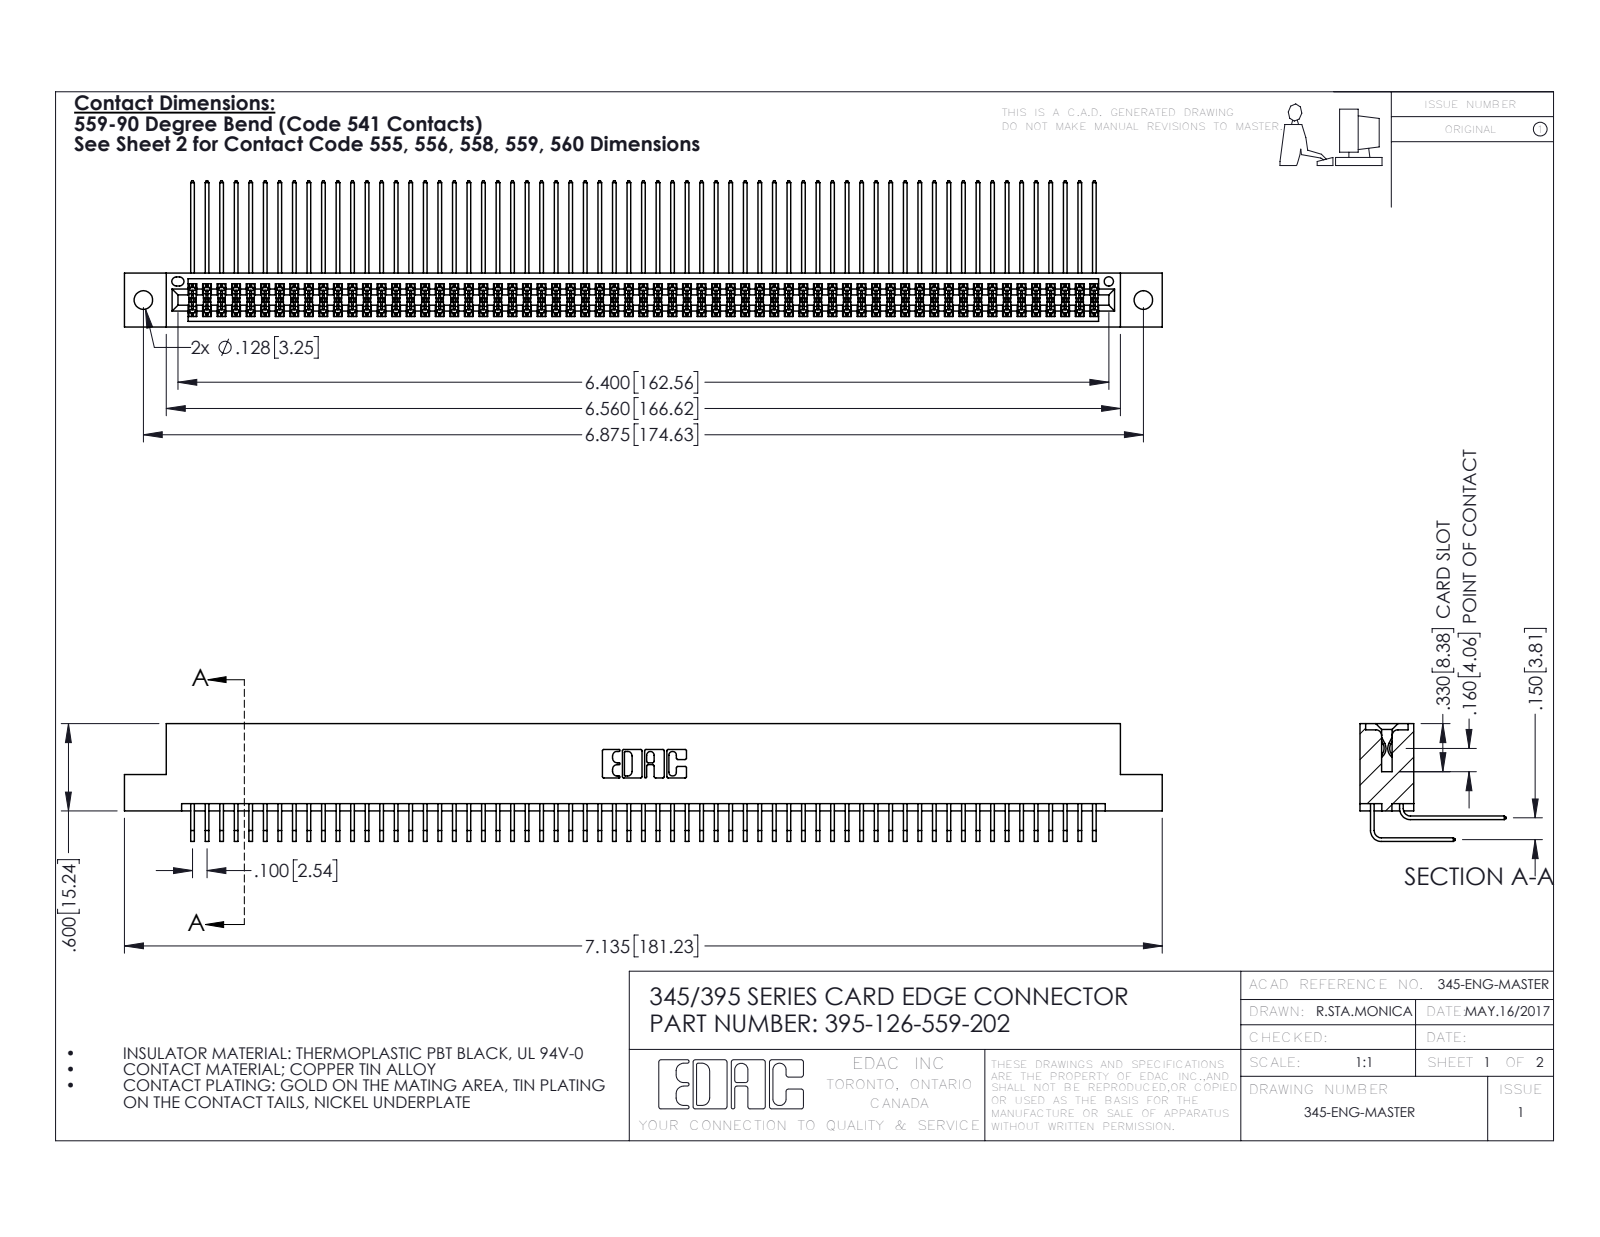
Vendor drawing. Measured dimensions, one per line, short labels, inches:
name: 345 Part_Flush Mounting Lugs - 0.128 Dia; 395-126-559-202; 345-292-001_558 559 Tail - 1; 345-292-001_559 Tail - 2
written by: SolidWorks 2016 (CONFIG_CONTROL_DESIGN)
unit: in
bodies: 127 solids, 6678 faces (4490 planar, 2188 cylindrical, 0 other)
size: 7.135 × 1.005 × 0.809
volume: 1.128 in³; area: 47.87 in²
holes: 2× ⌀0.128, 1× ⌀0.064
rounds: 190× R0.006, 22× R0.01, 6× R0.007, 6× R0.031, 3× R0.026, 2× R0.014, 2× R0.019, 2× R0.022
face distances: 0.072, 0.298, 0.2, 0.37, 0.098, 0.272, 0.025, 0.225, 0.175, 0.15
hole spacings: 0.27, 6.639, 6.875
